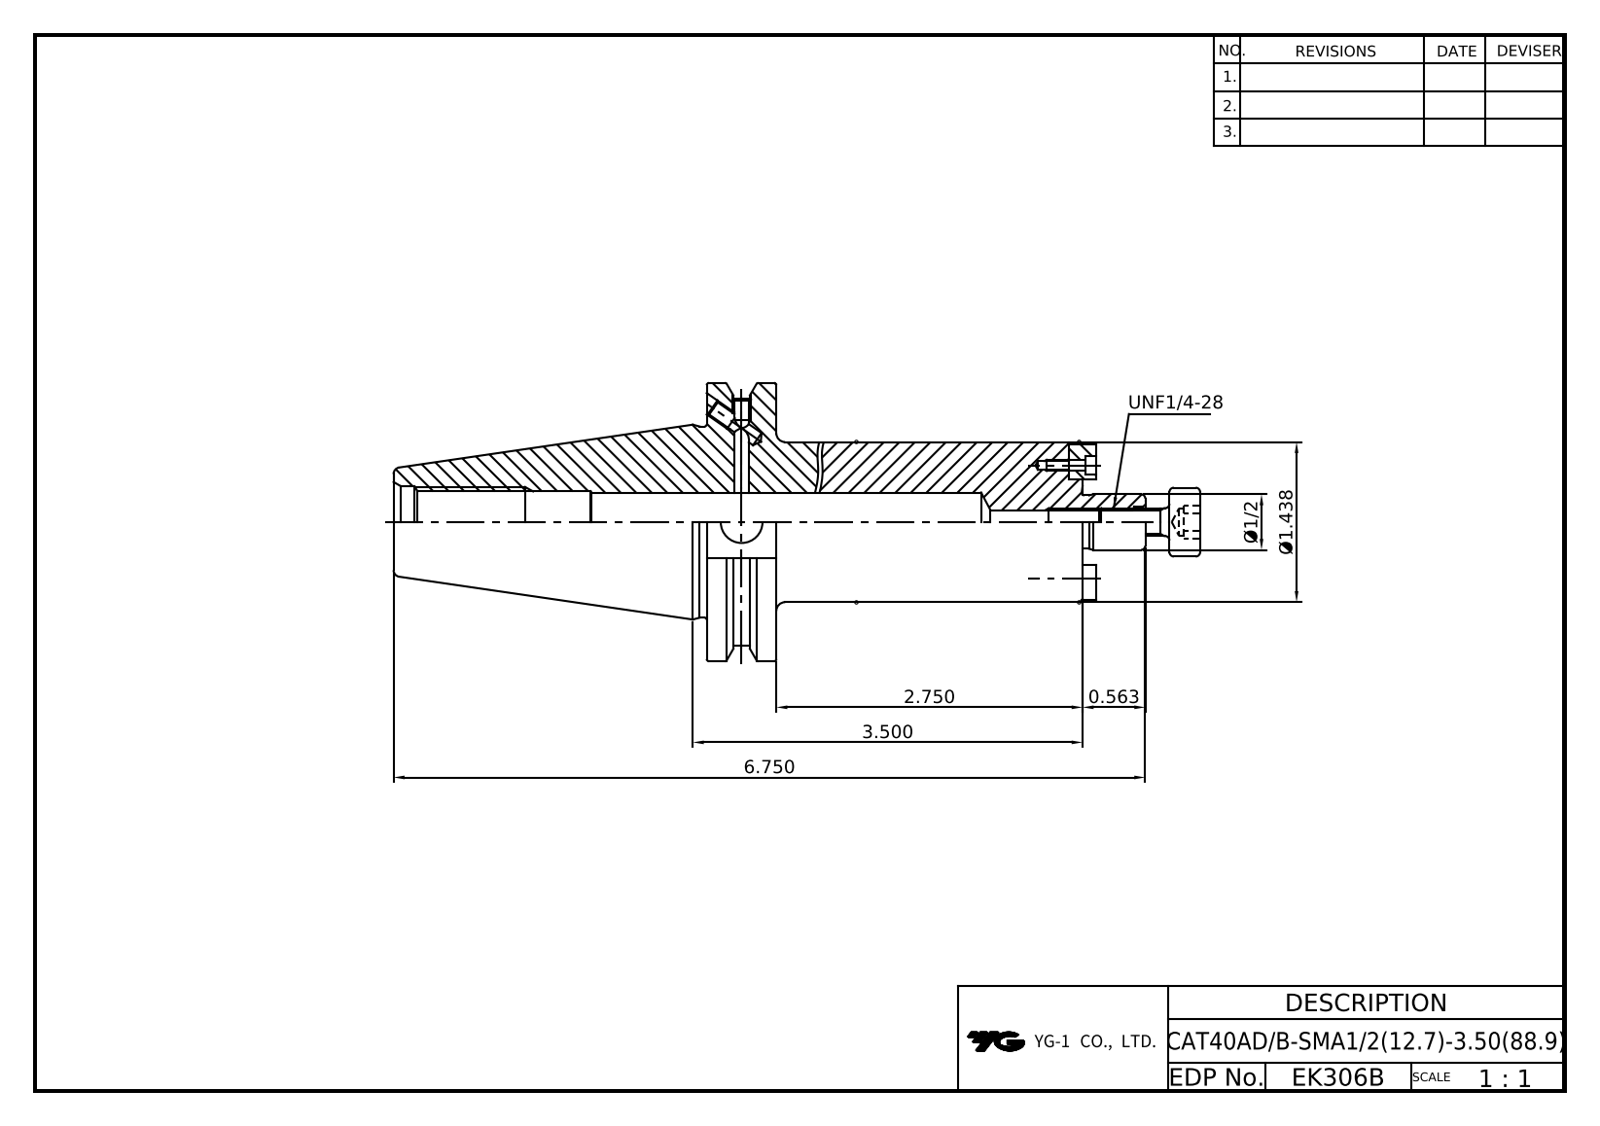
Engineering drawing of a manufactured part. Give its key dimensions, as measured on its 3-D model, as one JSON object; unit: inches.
{"part_name": "LO-CAT40ADB-SMA12.7-88.9; HEX'' WRENCH BOLT-UNC#3-48x1_4L; DRIVE KEY-6.35x6.35x8; COLLAR BOLT-UNF1_4-28x16L", "step_written_by": "Autodesk Inventor 2022 (AUTOMOTIVE_DESIGN)", "units": "inches", "bodies": {"solids": 6, "faces": 171, "planar": 88, "cylindrical": 46, "other": 37}, "overall_size": [7.327, 2.5, 2.405], "volume_in3": 10.41, "surface_area_in2": 52.64, "round_holes": [[0.128, 4], [0.165, 4], [0.076, 2], [0.102, 2], [0.157, 2], [0.211, 1], [0.25, 1], [0.276, 1], [0.375, 1], [0.512, 1], [0.527, 1], [0.642, 1]], "round_bosses_or_shafts": [[0.161, 2], [0.099, 2], [2.5, 1], [1.717, 1], [1.438, 1], [0.618, 1], [0.5, 1]], "partial_cylinders_radius": [[0.125, 2], [1.108, 1]], "face_to_face_distances": [0.625, 3.375, 2.75, 0.126, 3.249, 2.624, 1.874, 0.645, 2.812, 3.437], "hole_center_spacings": [0.47, 0.94]}
